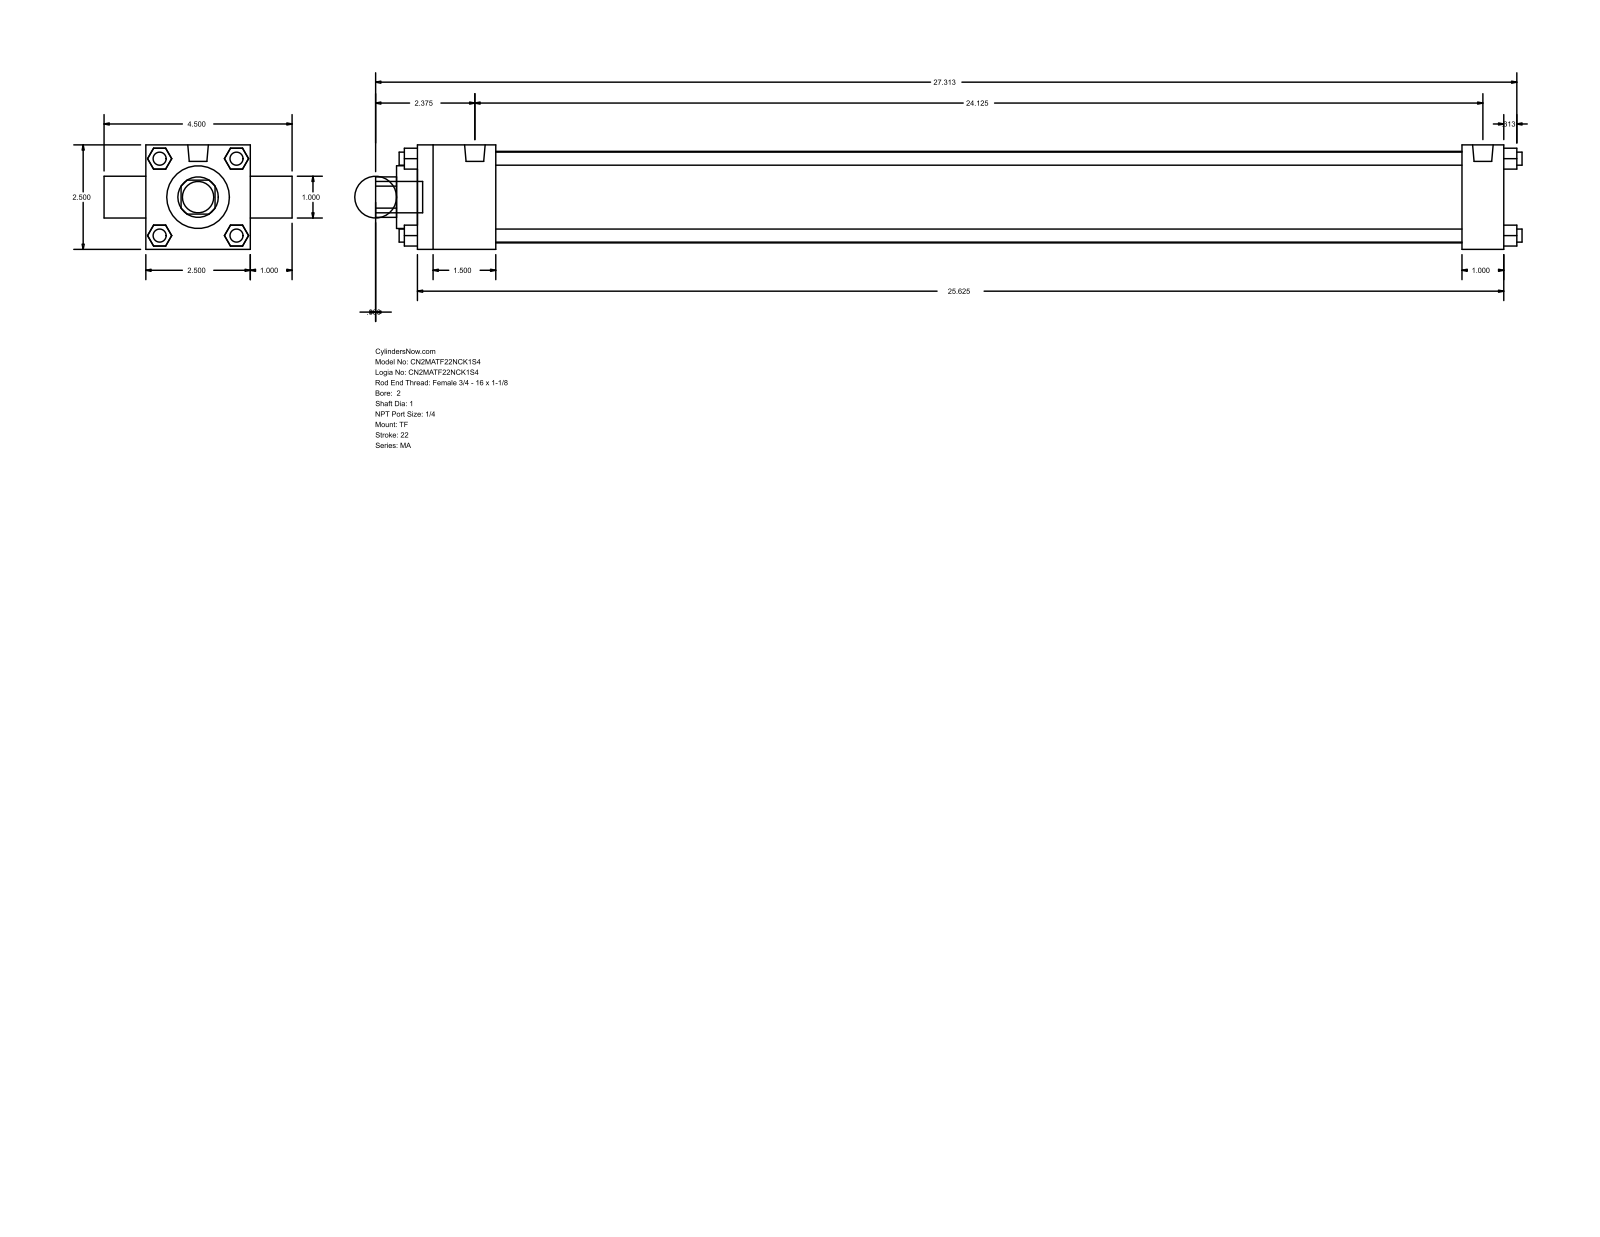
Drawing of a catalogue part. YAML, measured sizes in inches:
part_name: "MA_TF__0200_1"
step_written_by: "GSSL Pune (CONFIG_CONTROL_DESIGN)"
units: inches
bodies: {solids: 0, faces: 120, planar: 92, cylindrical: 28, other: 0}
overall_size: [27.437, 4.5, 2.5]
round_holes:
  - {diameter: 1, count: 2}
  - {diameter: 1.5, count: 1}
  - {diameter: 2.19, count: 1}
round_bosses_or_shafts:
  - {diameter: 0.313, count: 7}
  - {diameter: 0.492, count: 2}
  - {diameter: 0.75, count: 1}
partial_cylinders:
  - {radius: 0.484, count: 1}
face_to_face_distances: [2.5, 1, 26, 0.5, 1.875, 25, 23.125, 24.125, 3.5, 0.92]
